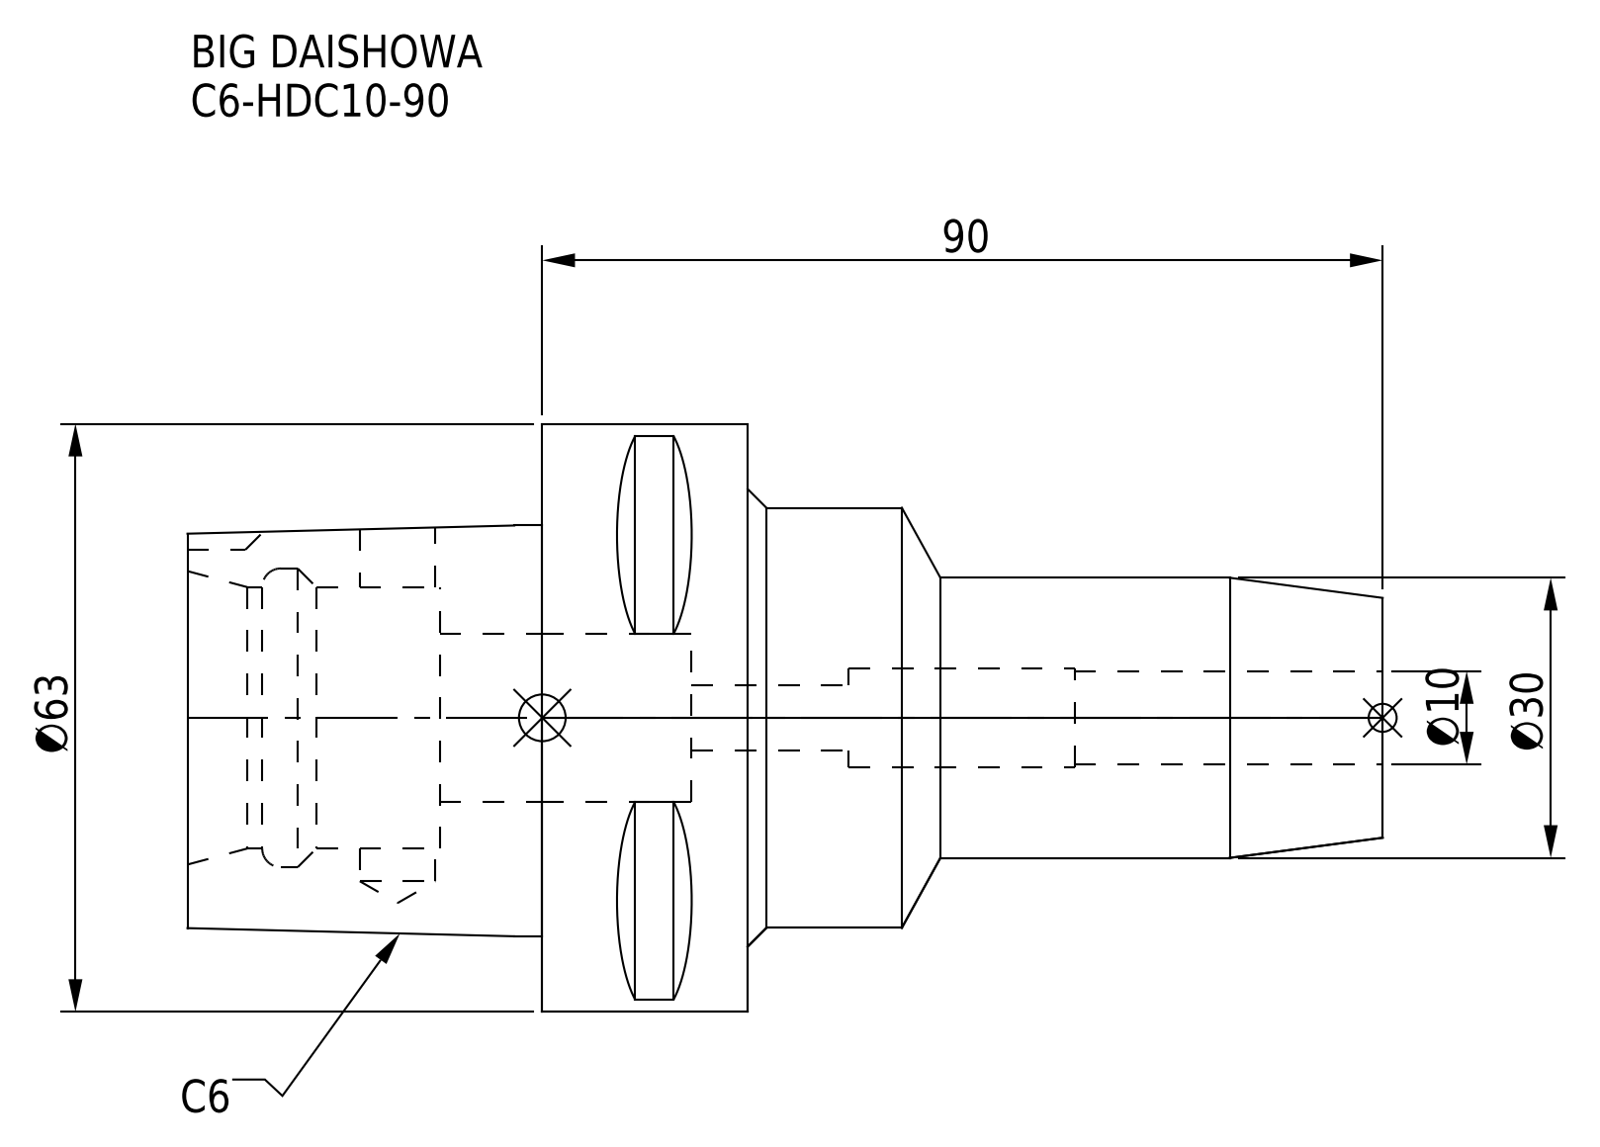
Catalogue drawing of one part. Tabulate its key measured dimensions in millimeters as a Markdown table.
| quantity | value |
| --- | --- |
| part name | C6-HDC10-90 |
| STEP written by | CREO PARAMETRIC BY PTC INC, 2016380 (AUTOMOTIVE_DESIGN) |
| units | millimeters |
| bodies | 1 solid, 71 faces (30 planar, 25 cylindrical, 16 other) |
| overall size | 128 × 63 × 63 |
| volume | 154 313 mm³ |
| surface area | 28 768 mm² |
| round holes (diameter × count) | 7 × 1, 8.1 × 1, 10 × 1, 10.5 × 1, 18 × 1, 28 × 1, 32 × 1 |
| round bosses / shafts (diameter × count) | 63 × 1, 45 × 1, 30 × 1 |
| partial cylindrical surfaces (radius × count) | 5 × 1 |
| main face-to-face distances | 22, 27, 60, 38, 68, 90, 128, 33, 101, 11 |
